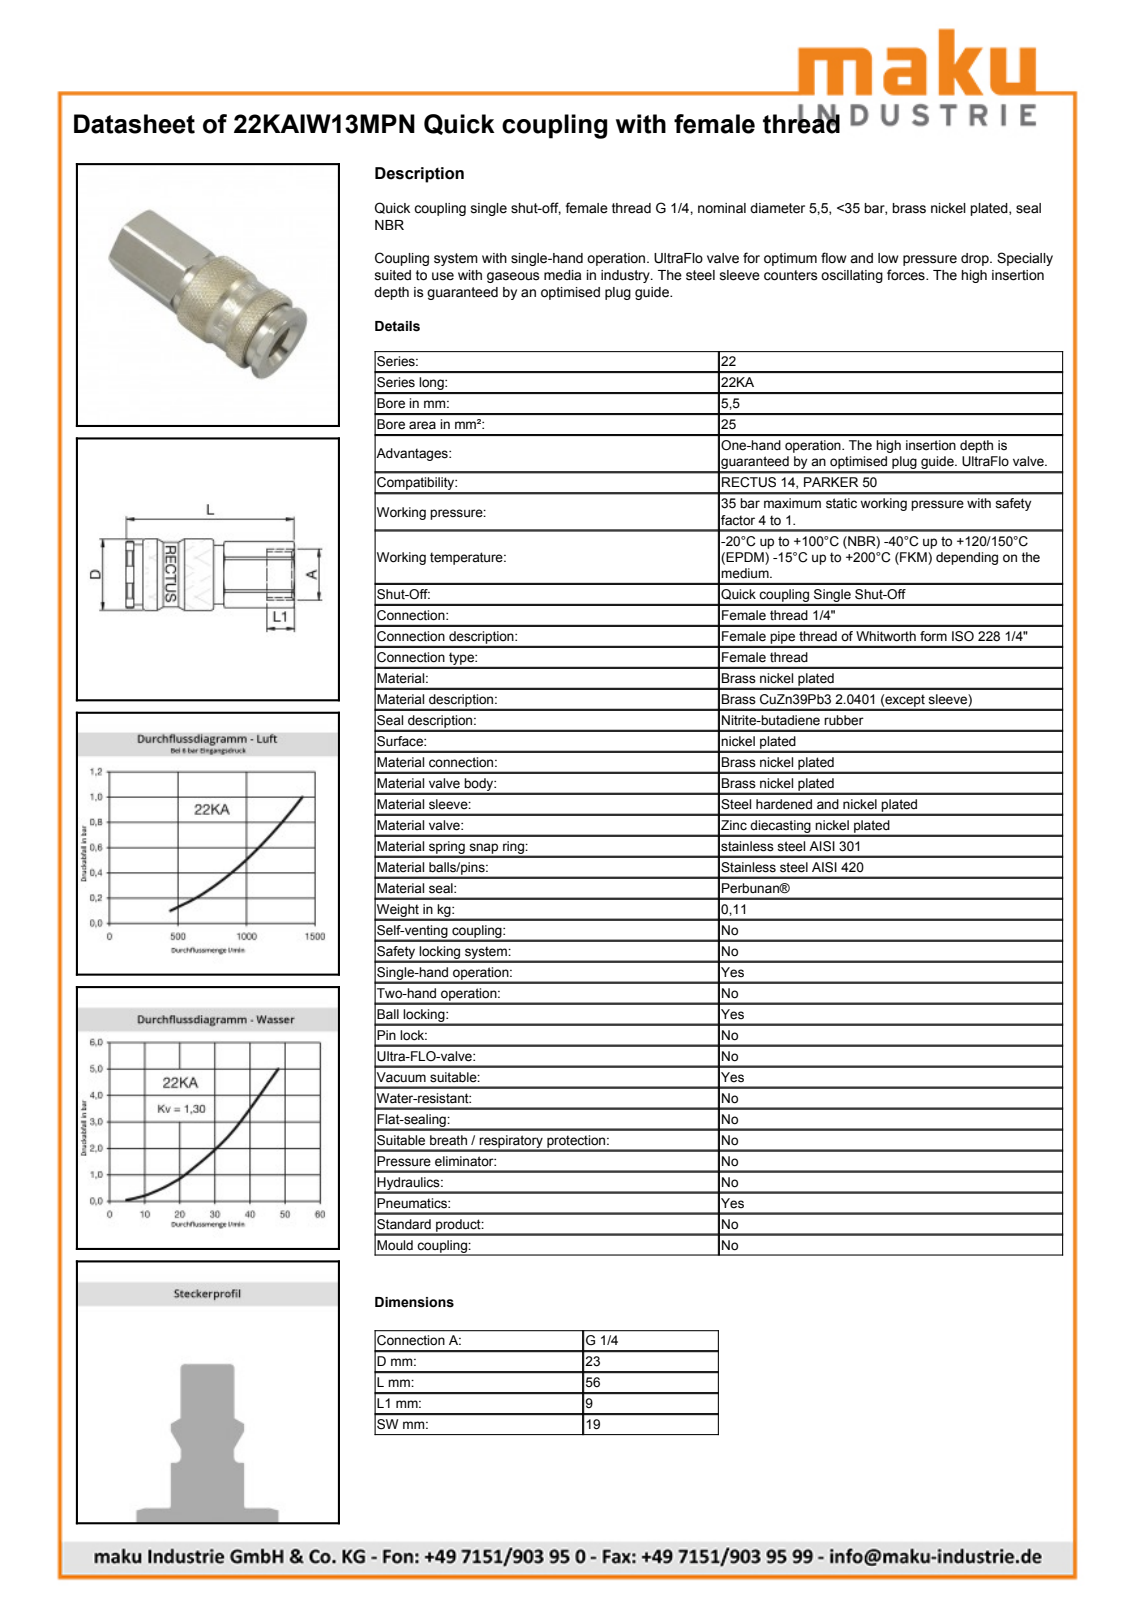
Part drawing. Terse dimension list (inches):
name: D108997
written by: Autodesk Inventor 2013 (AUTOMOTIVE_DESIGN)
unit: in
bodies: 2 solids, 533 faces (170 planar, 68 cylindrical, 295 other)
size: 2.189 × 0.911 × 0.911
volume: 1.042 in³; area: 12.59 in²
holes: 1× ⌀0.45, 1× ⌀0.63, 1× ⌀0.667, 1× ⌀0.762, 1× ⌀0.774
bosses: 1× ⌀0.911, 1× ⌀0.827, 1× ⌀0.764, 1× ⌀0.746, 1× ⌀0.615
rounds: 1× R0.409, 1× R0.421, 1× R0.433
face distances: 0.748, 2.189, 0.827, 1.795, 0.394, 0.787, 1.008, 1.402, 0.969, 0.181
